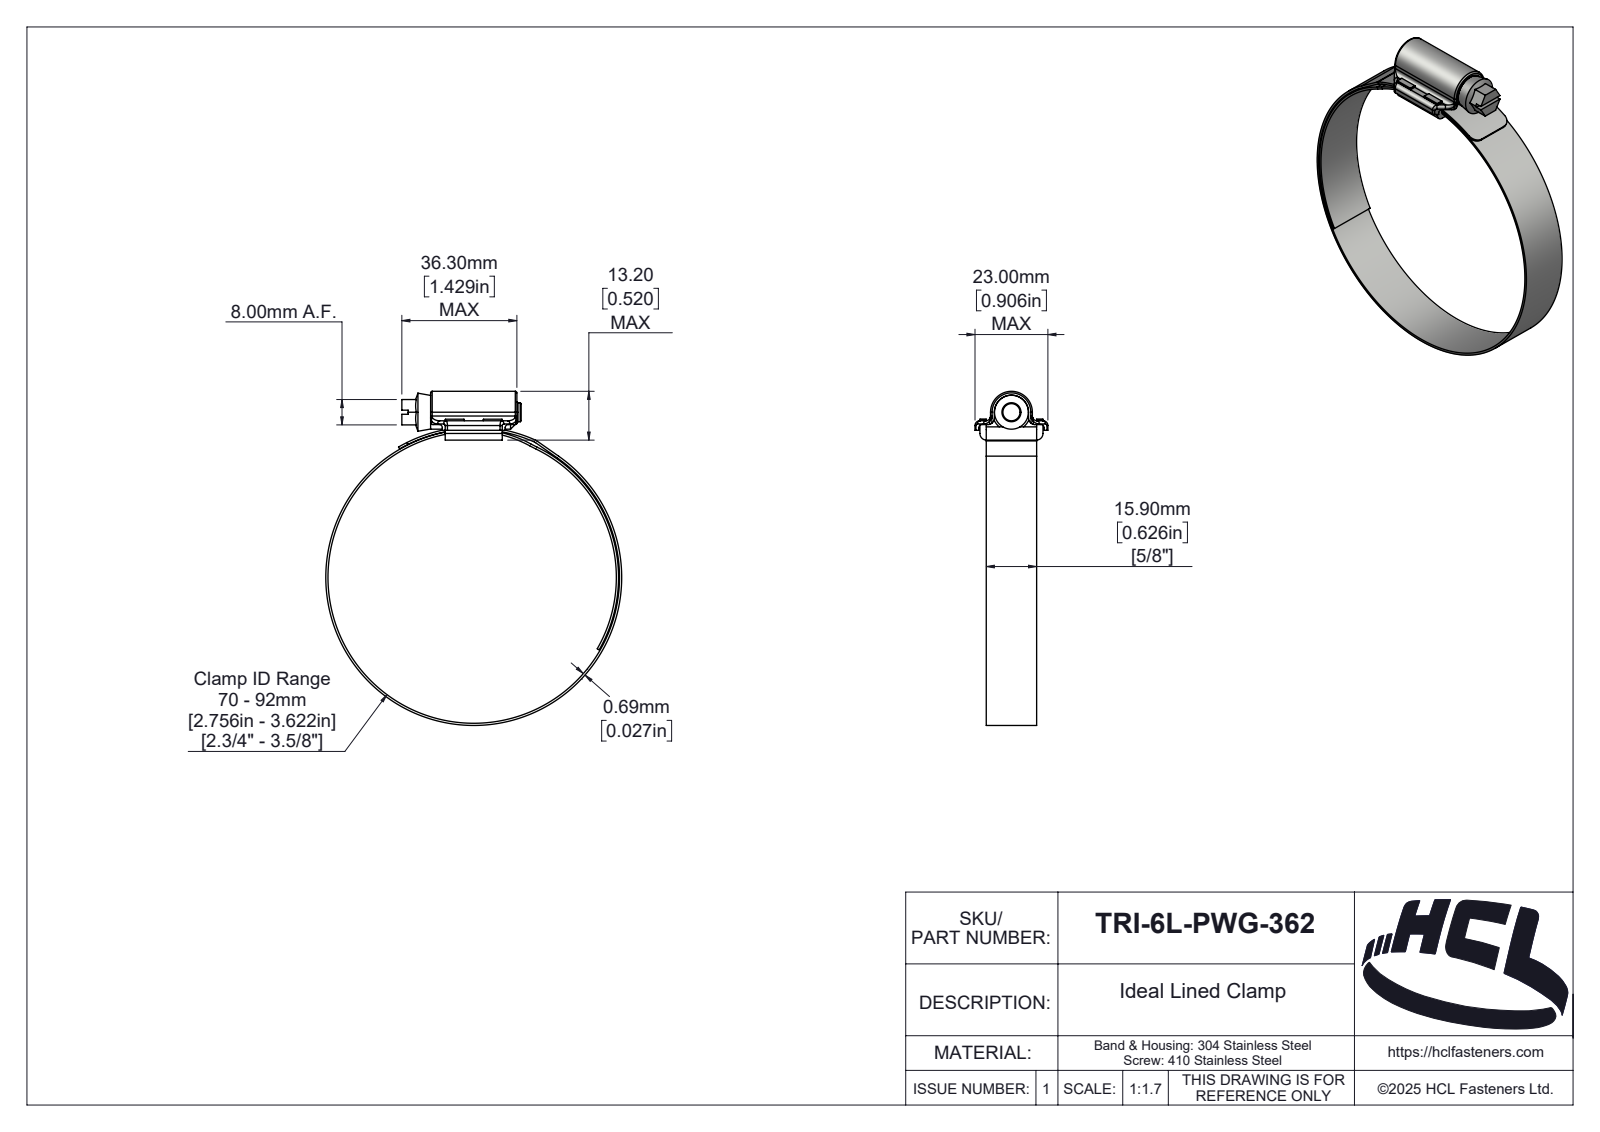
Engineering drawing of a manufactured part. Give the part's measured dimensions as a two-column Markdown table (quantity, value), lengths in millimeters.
| quantity | value |
| --- | --- |
| part name | TRI-6L-PWG-362 |
| STEP written by | SolidWorks 2025 (AUTOMOTIVE_DESIGN) |
| units | millimeters |
| bodies | 4 solids, 268 faces (87 planar, 102 cylindrical, 79 other) |
| overall size | 105.39 × 93.38 × 23 |
| volume | 9 707 mm³ |
| surface area | 18 257 mm² |
| round holes (diameter × count) | 92 × 1 |
| round bosses / shafts (diameter × count) | 93.38 × 1, 10.7 × 1, 6 × 1 |
| partial cylindrical surfaces (radius × count) | 1 × 14, 0.5 × 4, 1.5 × 4, 2 × 3, 0.1 × 2, 2.1 × 2, 3 × 2, 0.46 × 1 |
| main face-to-face distances | 2, 15.9, 17.9, 4.9, 0.69, 1.2, 4.55, 3.35, 15.35, 2.55 |
